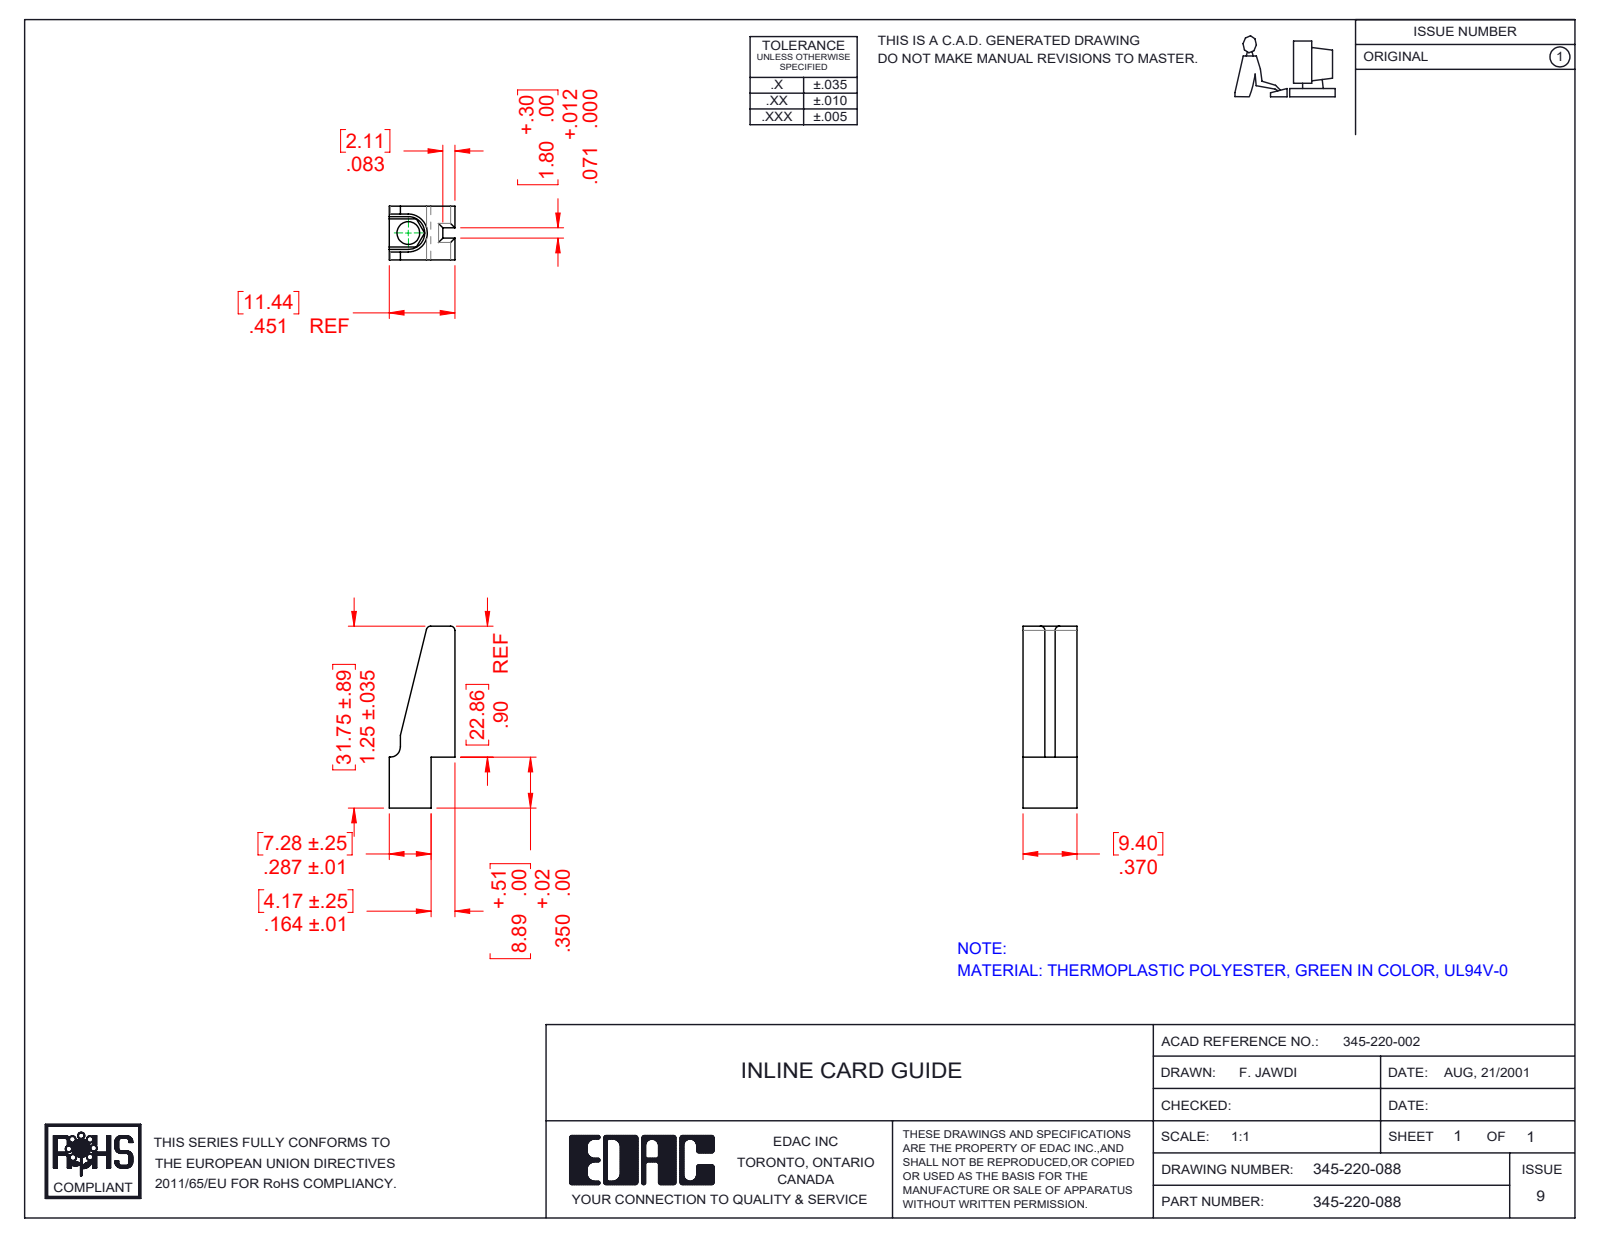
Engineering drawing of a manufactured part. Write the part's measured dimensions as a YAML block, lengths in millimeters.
part_name: "345-220-088"
step_written_by: "SolidWorks 2020 (AUTOMOTIVE_DESIGN)"
units: millimeters
bodies: {solids: 1, faces: 39, planar: 27, cylindrical: 12, other: 0}
overall_size: [31.8, 11.5, 9.4]
volume: 1600
surface_area: 1497
round_holes:
  - {diameter: 4, count: 1}
partial_cylinders:
  - {radius: 0.8, count: 5}
  - {radius: 1.8, count: 1}
  - {radius: 2.8, count: 1}
  - {radius: 3.3, count: 1}
face_to_face_distances: [9.4, 3.8, 5.6, 4.2, 7.3, 11.4, 1.8, 8.9, 9.3, 2.1]
